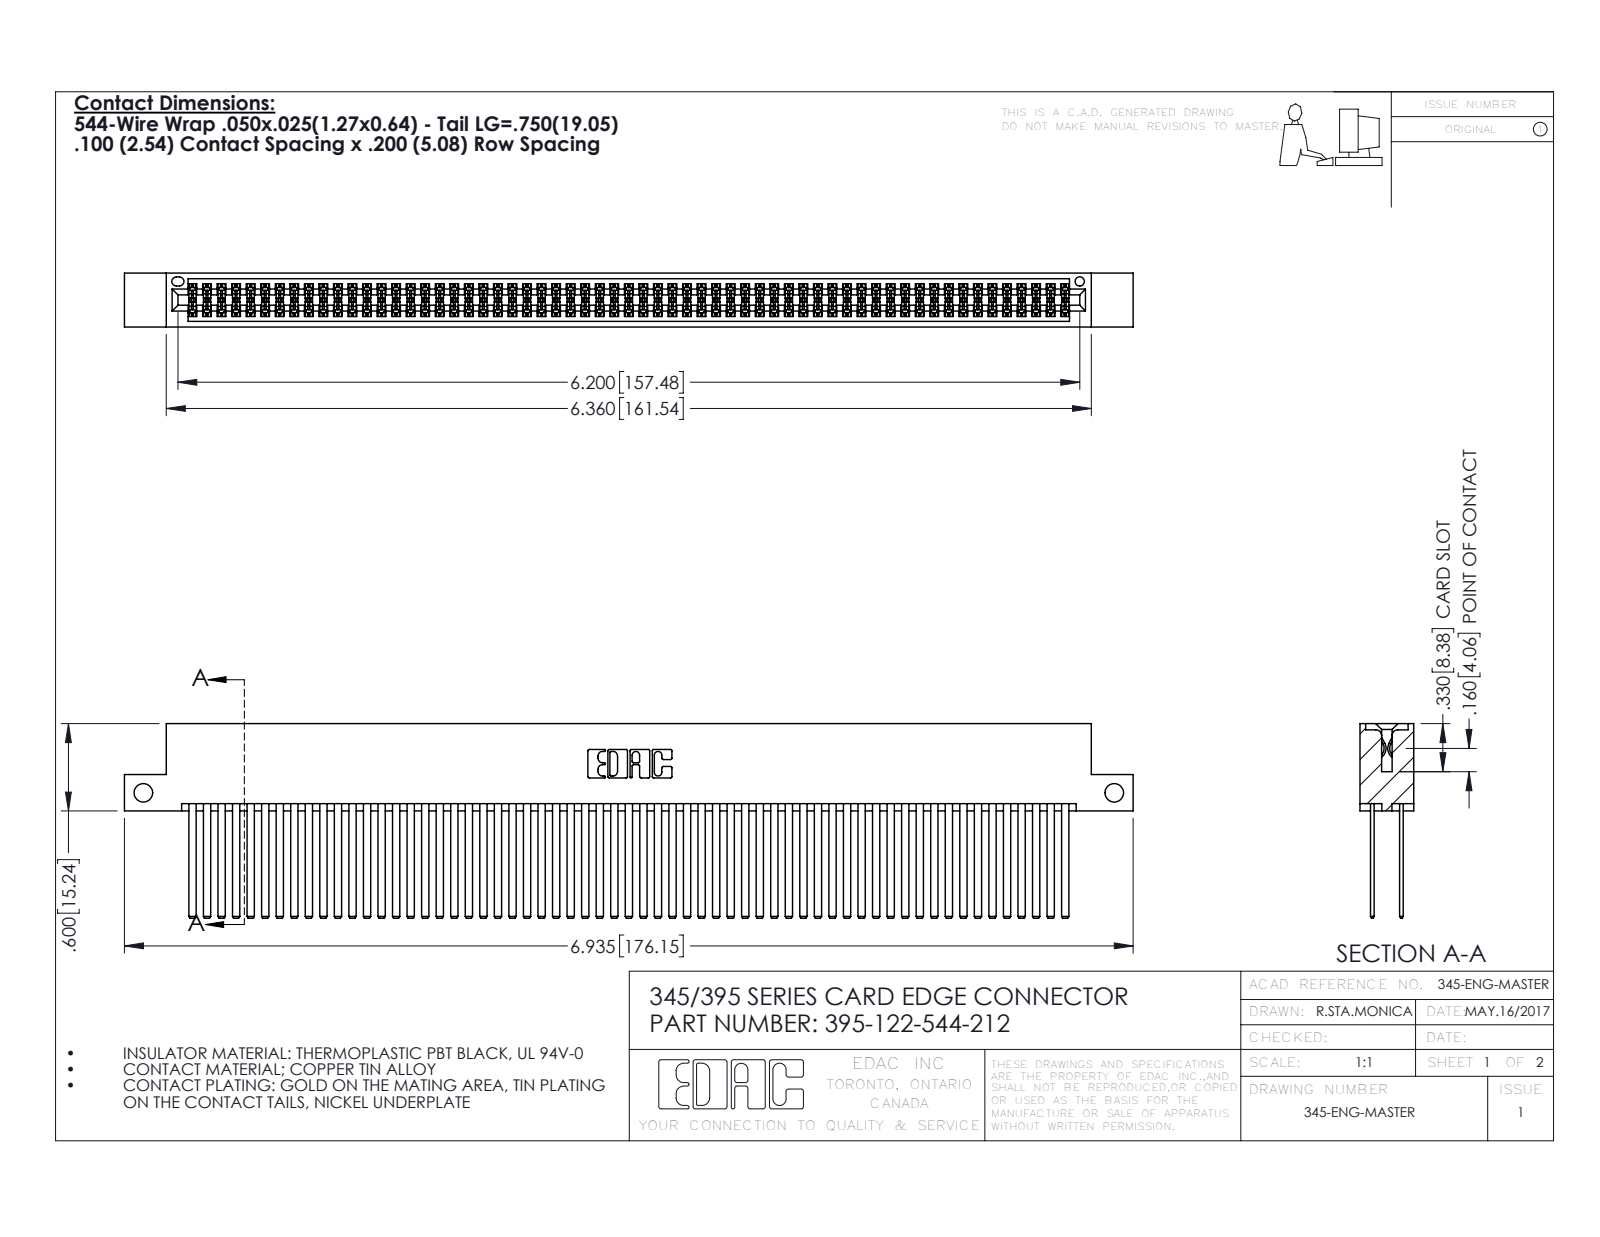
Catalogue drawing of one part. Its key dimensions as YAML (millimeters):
part_name: "345 Part_Flush Mounting Lugs - Side Mount; 345-292-001_345-293-144; 395-122-544-212"
step_written_by: "SolidWorks 2016 (CONFIG_CONTROL_DESIGN)"
units: millimeters
bodies: {solids: 123, faces: 5494, planar: 3618, cylindrical: 1876, other: 0}
overall_size: [176.1, 34, 9.4]
volume: 18910
surface_area: 33200
round_holes:
  - {diameter: 3.3, count: 2}
  - {diameter: 1.6, count: 1}
partial_cylinders:
  - {radius: 0.2, count: 183}
  - {radius: 0.3, count: 22}
  - {radius: 0.2, count: 6}
  - {radius: 0.8, count: 6}
  - {radius: 0.7, count: 3}
  - {radius: 0.4, count: 2}
  - {radius: 0.5, count: 2}
  - {radius: 0.6, count: 2}
face_to_face_distances: [5.1, 0.6, 7.6, 1.8, 2.5, 6.9, 5.7, 4.4, 9.4, 1.3]
hole_center_spacings: [169.5]
